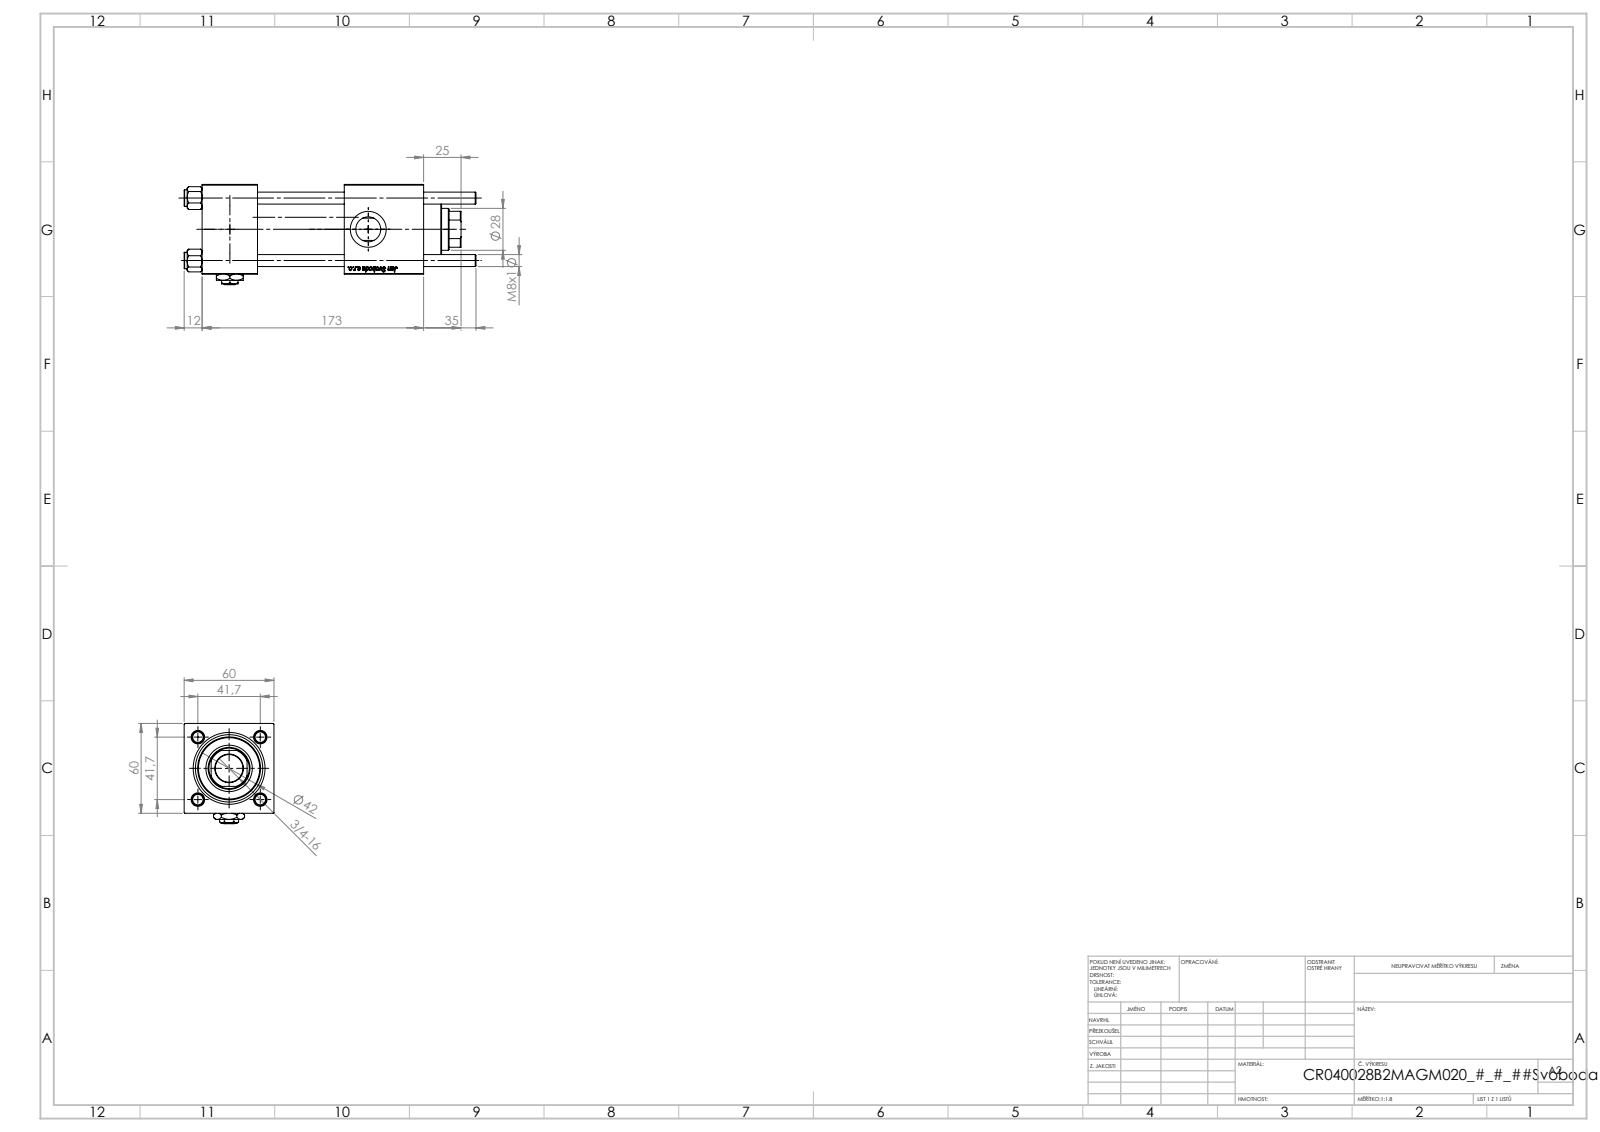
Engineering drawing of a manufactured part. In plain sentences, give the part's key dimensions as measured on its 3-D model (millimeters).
The part is named "V215CR_VCP_B; V215CR_B_TYCINKA; Zatka_pro_OIL_PORT; V215CR_B-1 (+2 more)". Its 3-D file was written by "SolidWorks 2019 (CONFIG_CONTROL_DESIGN)". It is 12 solids with 1212 faces: 456 planar, 86 cylindrical and 670 other. Overall it measures 195 by 67 by 60 millimeters. Its volume is 433 517 cubic millimeters and its surface area 121 708 square millimeters. Round holes: 4 of diameter 8, 2 of diameter 7, 2 of diameter 16.66, 2 of diameter 24, 1 of diameter 16, 1 of diameter 18.5, 1 of diameter 28, 1 of diameter 31, 1 of diameter 40, 1 of diameter 45. Round bosses or shafts: 4 of diameter 11, 1 of diameter 46, 1 of diameter 42. Partial cylindrical surfaces (rounded edges, fillets, slot ends): 1 of radius 13.5. The main face-to-face distances are 60, 37, 58, 95, 119.3, 82.3, 24.3, 53, 148, 111. The hole center spacings are 29.49, 41.7, 58.97.
